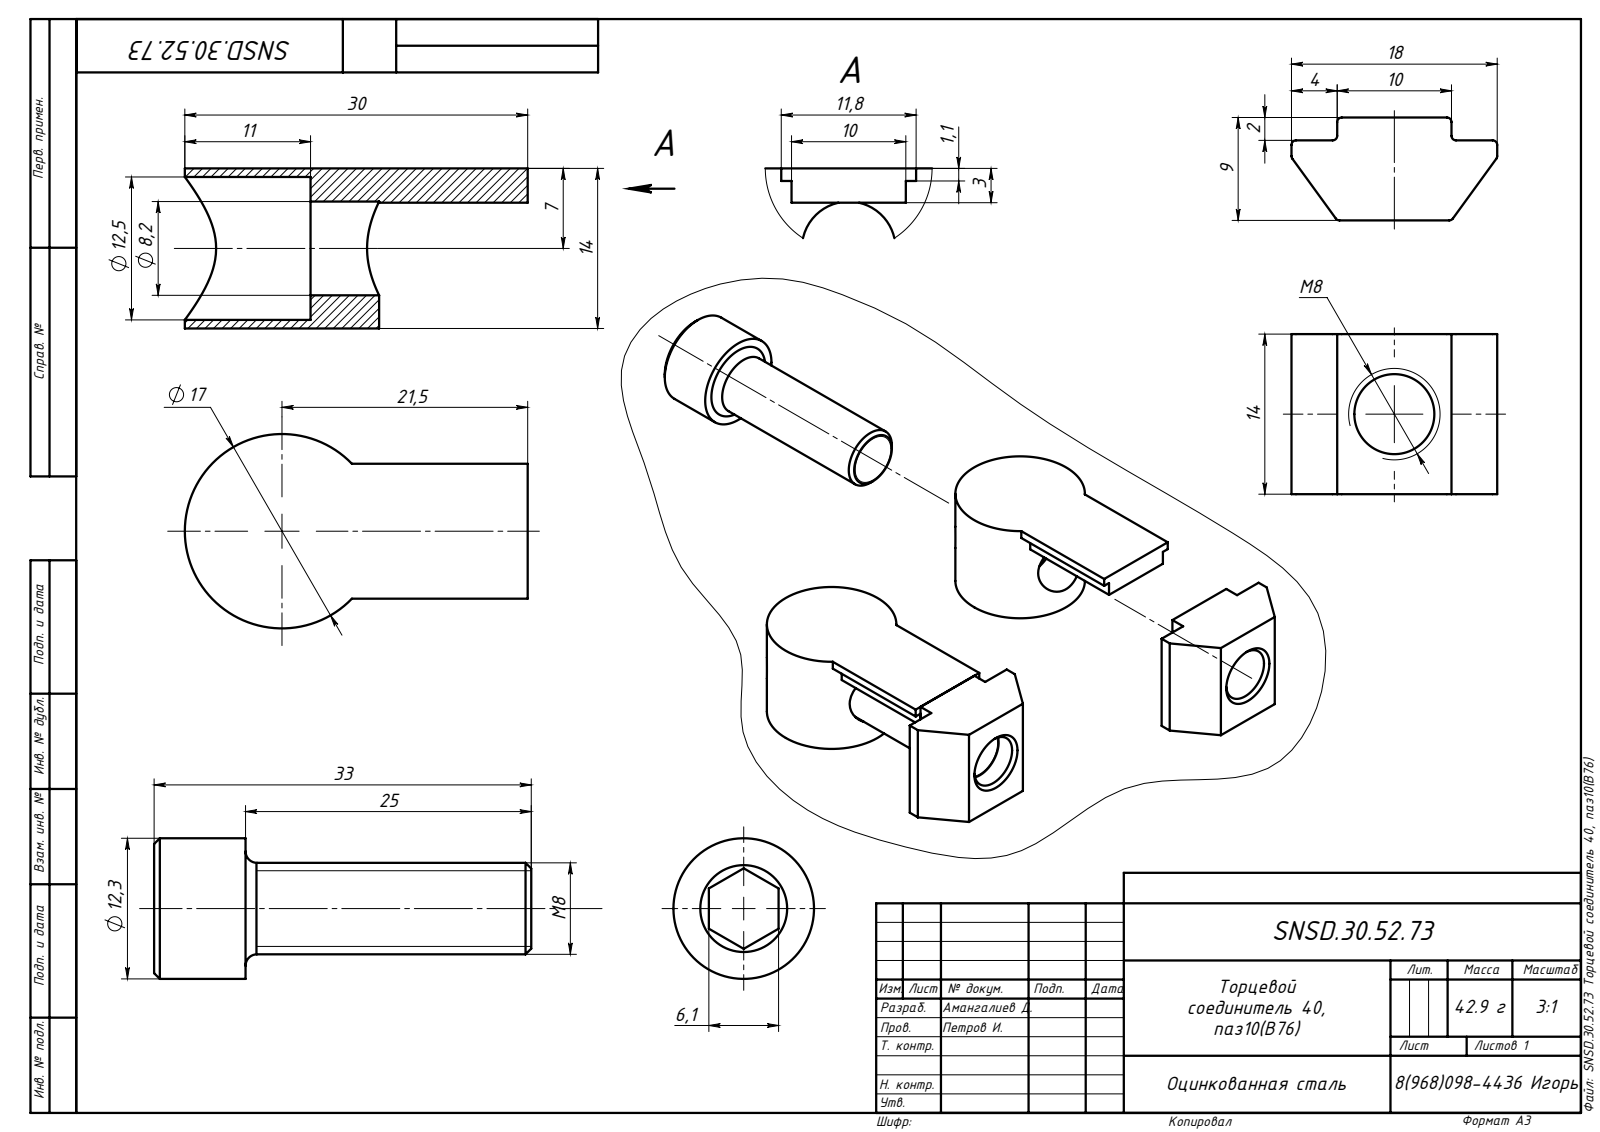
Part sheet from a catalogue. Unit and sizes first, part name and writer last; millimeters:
Units: millimetres
Overall size (bounding box): 39 × 18 × 14
Round holes (diameter × count): ⌀7 ×1, ⌀8.2 ×1, ⌀12.5 ×1
Round bosses / shafts (diameter × count): ⌀17 ×1, ⌀12.3 ×1, ⌀8 ×1
Main face-to-face distances: 14, 3, 11, 2, 19, 21, 28, 9, 7, 4
Volume: 5 455 mm³ · Surface area: 4 308 mm²
Bodies: 3 solids, 59 faces (34 planar, 13 cylindrical, 12 other)
STEP written by: SolidWorks 2014 (AUTOMOTIVE_DESIGN)
